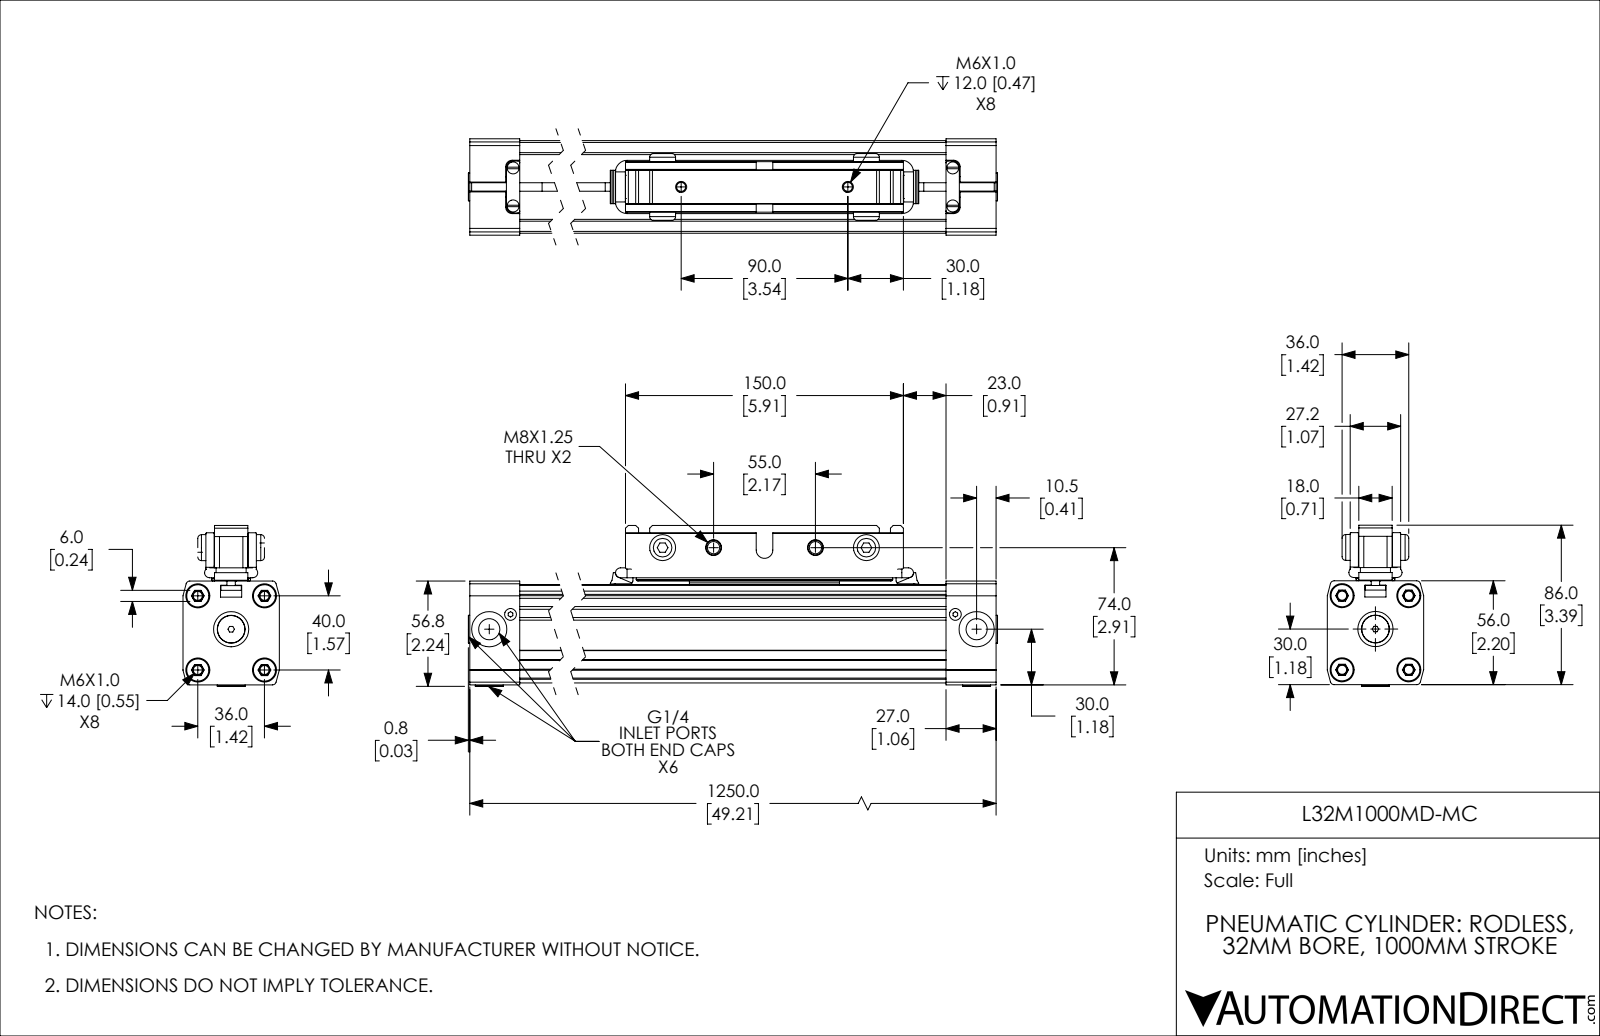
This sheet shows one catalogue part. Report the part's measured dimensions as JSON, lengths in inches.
{"part_name": "L32M1000MD-MC_PISTON; L32M1000MD-MC; L32M1000MD-MC_BODY", "step_written_by": "SolidWorks 2019 (CONFIG_CONTROL_DESIGN)", "units": "inches", "bodies": {"solids": 13, "faces": 822, "planar": 433, "cylindrical": 273, "other": 116}, "overall_size": [49.274, 3.417, 2.047], "volume_in3": 136.3, "surface_area_in2": 825.7, "round_holes": [[0.194, 6], [0.451, 5], [0.748, 5], [0.256, 4], [0.262, 4], [0.339, 4], [0.512, 4], [0.252, 2], [1.264, 1]], "round_bosses_or_shafts": [[0.472, 4], [0.21, 4], [0.591, 3], [0.383, 3], [0.323, 3], [0.551, 2], [1.26, 1], [1.252, 1]], "partial_cylinders_radius": [[0.039, 22], [0.079, 18], [0.138, 8], [0.012, 4], [0.02, 4], [0.024, 4], [0.157, 4], [0.006, 2]], "face_to_face_distances": [2.087, 1.969, 0.201, 1.072, 0.894, 1.075, 1.768, 0.454, 0.253, 0.181], "hole_center_spacings": [0.649, 47.88, 0.552, 0.807, 0.935, 1.002, 1.083, 1.119]}
